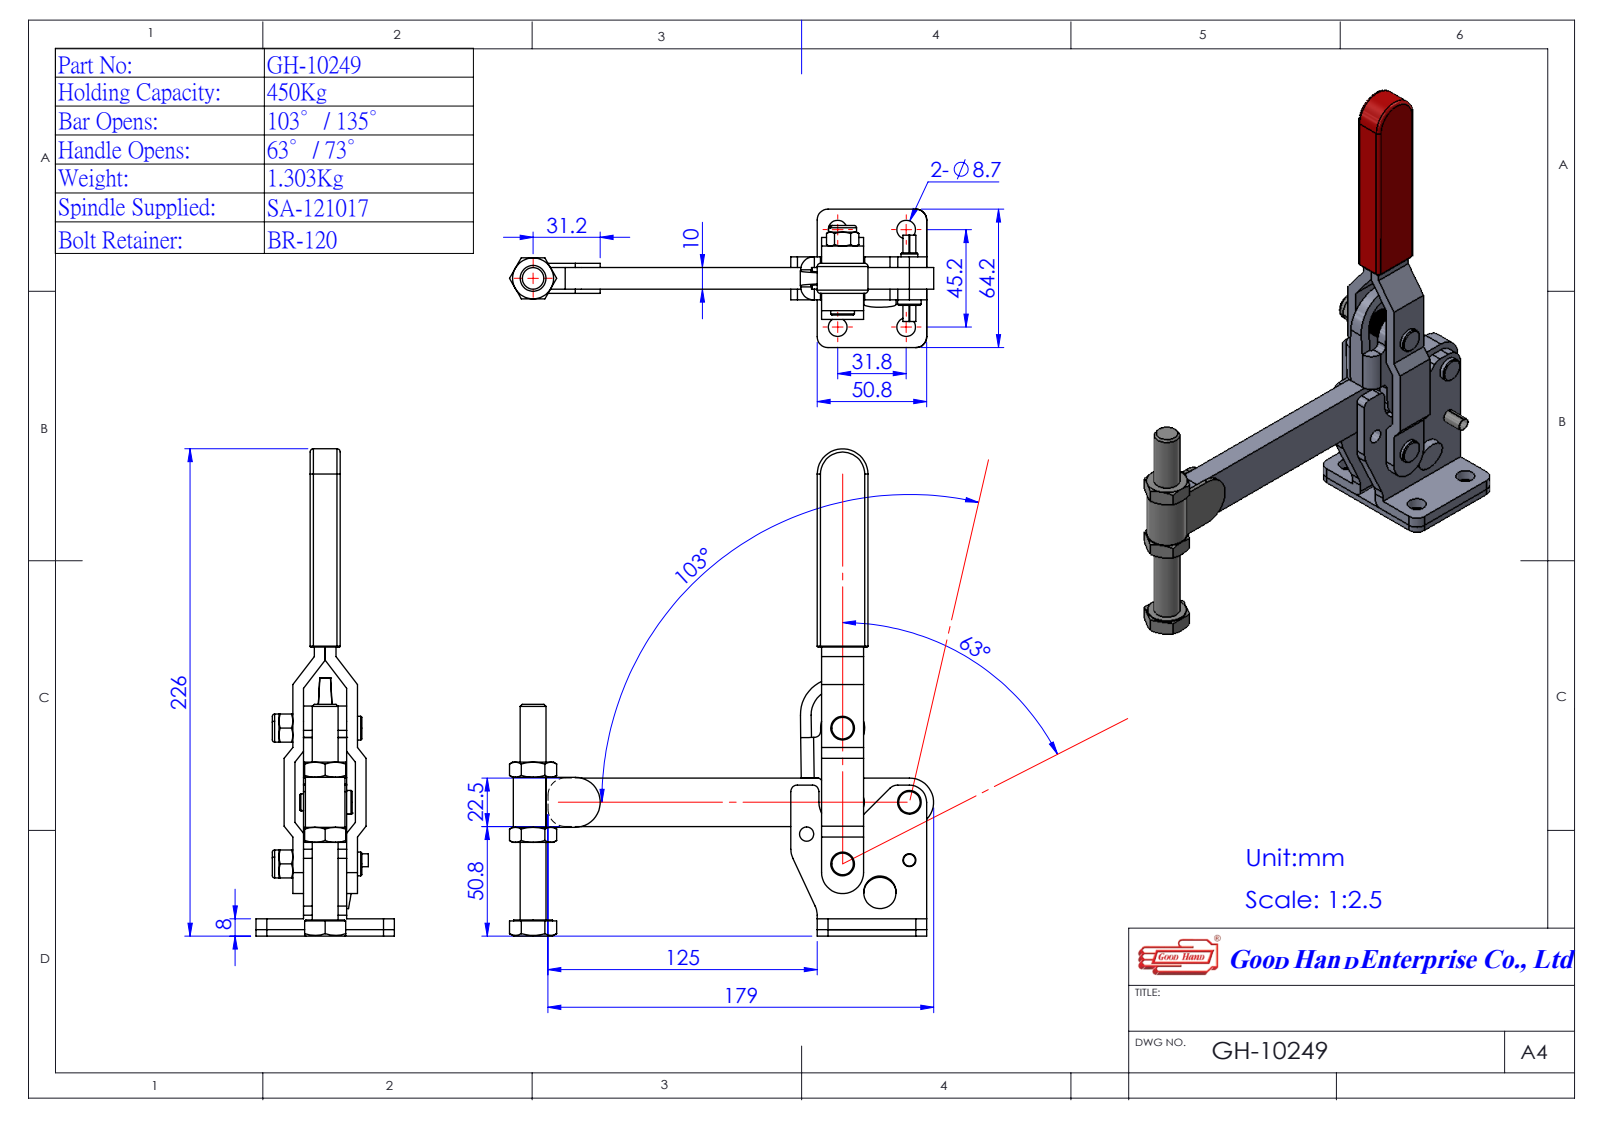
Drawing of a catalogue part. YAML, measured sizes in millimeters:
part_name: "Group2^GH-10249(簡化); GH-10249(簡化); Group5^GH-10249(簡化); Group1^GH-10249(簡化) (+2 more)"
step_written_by: "SolidWorks 2016 (AUTOMOTIVE_DESIGN)"
units: millimeters
bodies: {solids: 4, faces: 320, planar: 132, cylindrical: 128, other: 60}
overall_size: [226, 212.06, 64.2]
volume: 159718
surface_area: 75011
round_holes:
  - {diameter: 6, count: 4}
  - {diameter: 8.7, count: 4}
  - {diameter: 5.5, count: 1}
  - {diameter: 6.6, count: 1}
  - {diameter: 10.2, count: 1}
  - {diameter: 12, count: 1}
round_bosses_or_shafts:
  - {diameter: 11, count: 4}
  - {diameter: 7.94, count: 2}
  - {diameter: 7.8, count: 2}
  - {diameter: 6, count: 1}
partial_cylinders:
  - {radius: 5, count: 9}
  - {radius: 0.5, count: 4}
  - {radius: 1, count: 4}
  - {radius: 1.5, count: 4}
  - {radius: 3, count: 4}
  - {radius: 7.15, count: 1}
  - {radius: 8, count: 1}
  - {radius: 9.5, count: 1}
face_to_face_distances: [5, 10, 15, 2, 20, 3, 12, 8, 17, 14]
hole_center_spacings: [31.8, 45.2, 55.27, 158.16, 189.69, 21.7, 22.71, 26.85]
